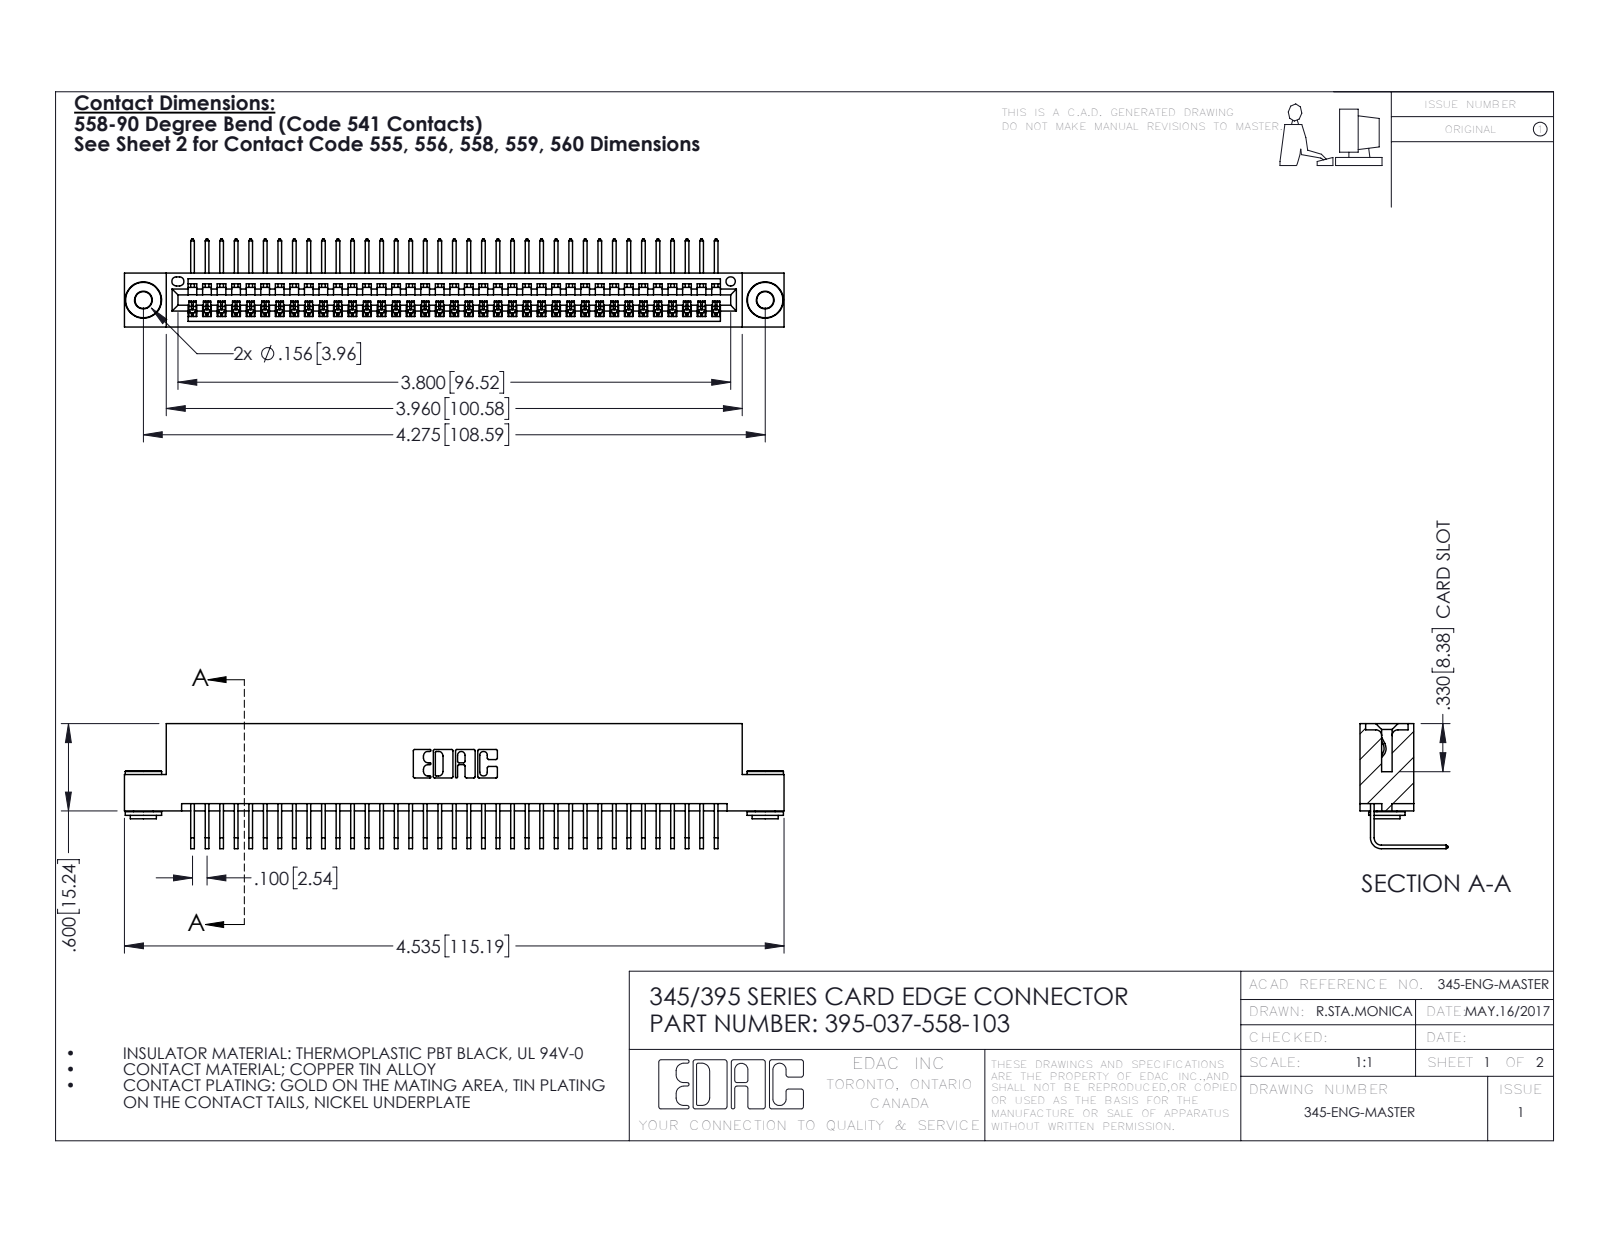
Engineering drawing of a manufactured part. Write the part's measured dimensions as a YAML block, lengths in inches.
part_name: "345-250-002_345-250-002-102; 345-292-001_558 Tail - 2; 395-037-558-103; 345 Part_Flush Mounting Lugs - 0.156 Dia-TH"
step_written_by: "SolidWorks 2016 (CONFIG_CONTROL_DESIGN)"
units: inches
bodies: {solids: 40, faces: 2384, planar: 1644, cylindrical: 732, other: 8}
overall_size: [4.535, 0.859, 0.605]
volume: 0.674
surface_area: 24.1
round_holes:
  - {diameter: 0.116, count: 2}
  - {diameter: 0.156, count: 2}
  - {diameter: 0.064, count: 1}
round_bosses_or_shafts:
  - {diameter: 0.25, count: 2}
  - {diameter: 0.18, count: 2}
  - {diameter: 0.136, count: 2}
partial_cylinders:
  - {radius: 0.006, count: 74}
  - {radius: 0.01, count: 22}
  - {radius: 0.007, count: 6}
  - {radius: 0.031, count: 6}
  - {radius: 0.026, count: 3}
  - {radius: 0.031, count: 2}
  - {radius: 0.04, count: 2}
  - {radius: 0.014, count: 1}
face_to_face_distances: [0.072, 0.298, 0.2, 0.37, 0.025, 0.098, 0.272, 0.225, 0.149, 0.072]
hole_center_spacings: [0.27, 4.039, 4.275]
